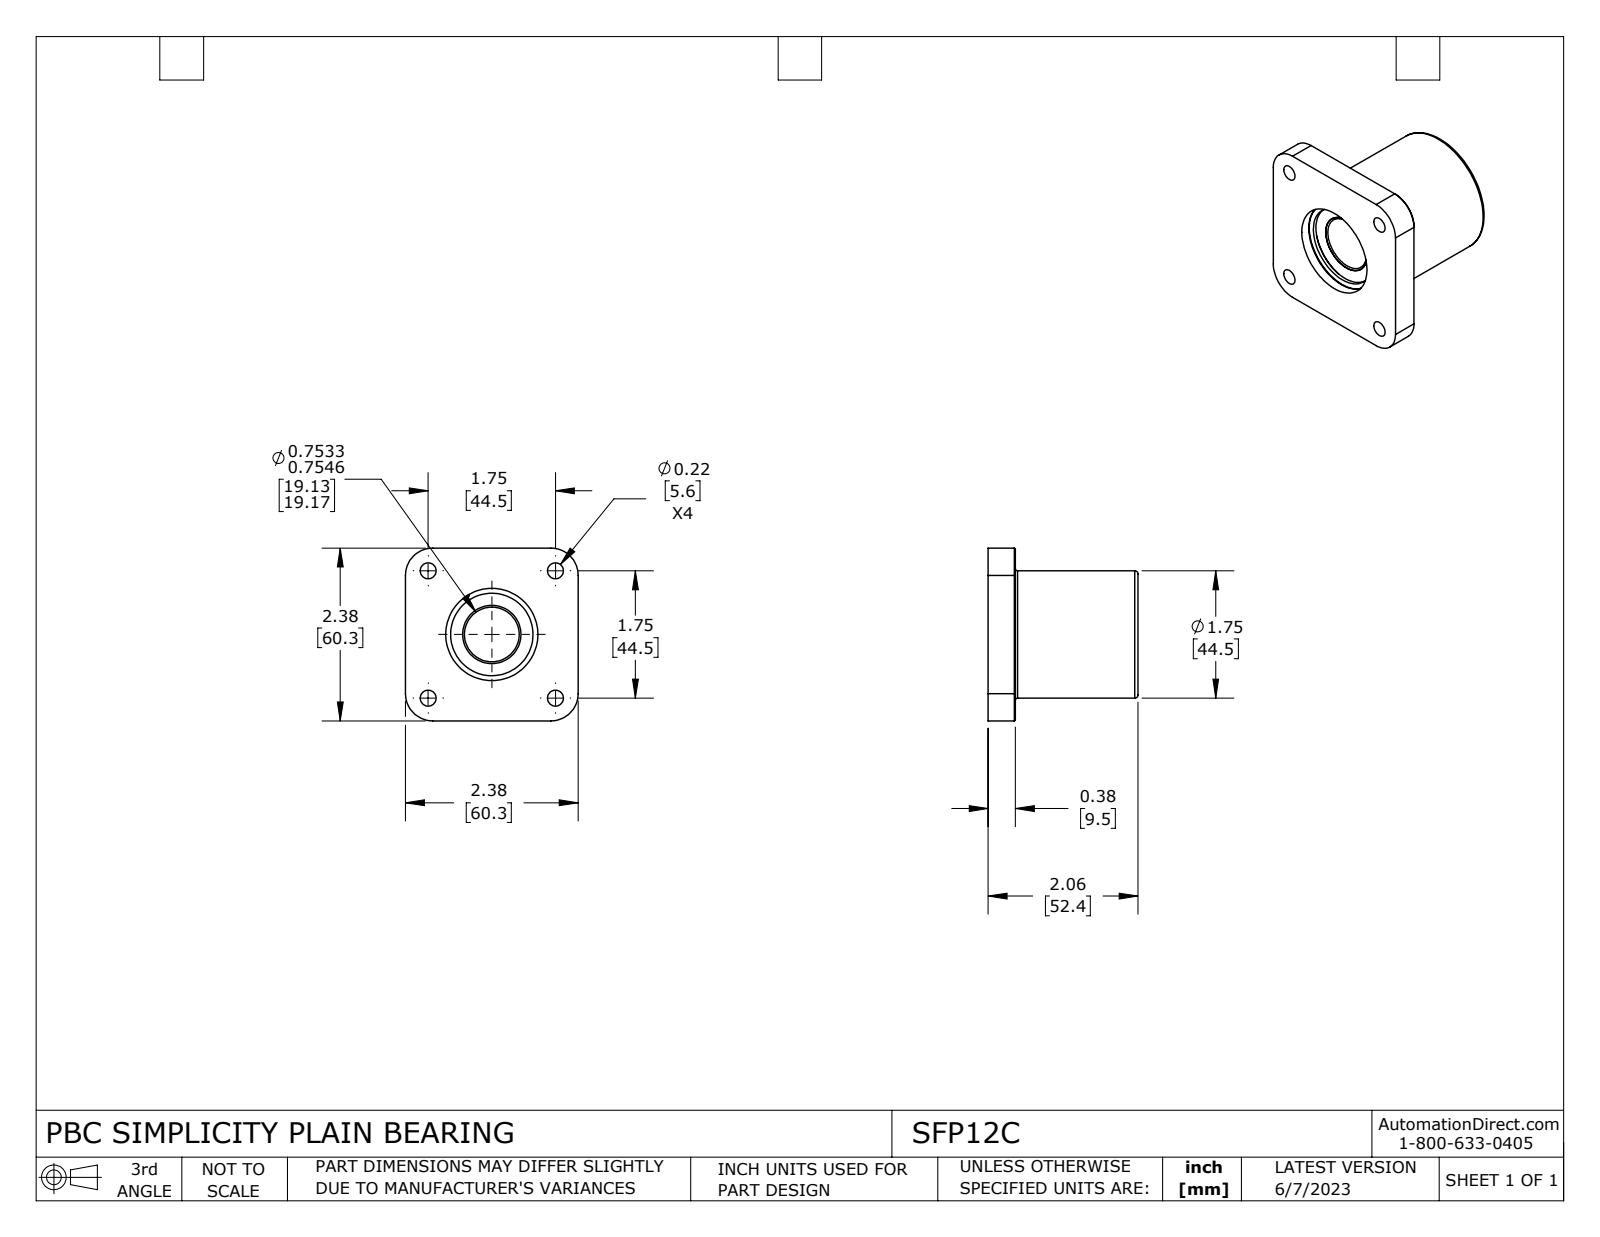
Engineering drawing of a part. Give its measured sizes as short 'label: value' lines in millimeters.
name: SFP12C
written by: SolidWorks 2021 (CONFIG_CONTROL_DESIGN)
unit: mm
bodies: 7 solids, 169 faces (41 planar, 74 cylindrical, 54 other)
size: 60.3 × 60.3 × 52.4
volume: 77 690 mm³; area: 36 250 mm²
holes: 4× ⌀5.6, 1× ⌀19.1, 1× ⌀20.4, 1× ⌀28.8, 1× ⌀32.2, 1× ⌀33.8
bosses: 1× ⌀44.5, 1× ⌀34, 1× ⌀31.7, 1× ⌀29.9, 1× ⌀27.6
rounds: 4× R0.4, 4× R9.5, 2× R0.3, 2× R0.6
face distances: 9.5, 60.3, 4, 48.4, 5.3, 47.1, 1.3, 43.1, 52.4, 42.8
hole spacings: 31.4, 44.5, 62.9
